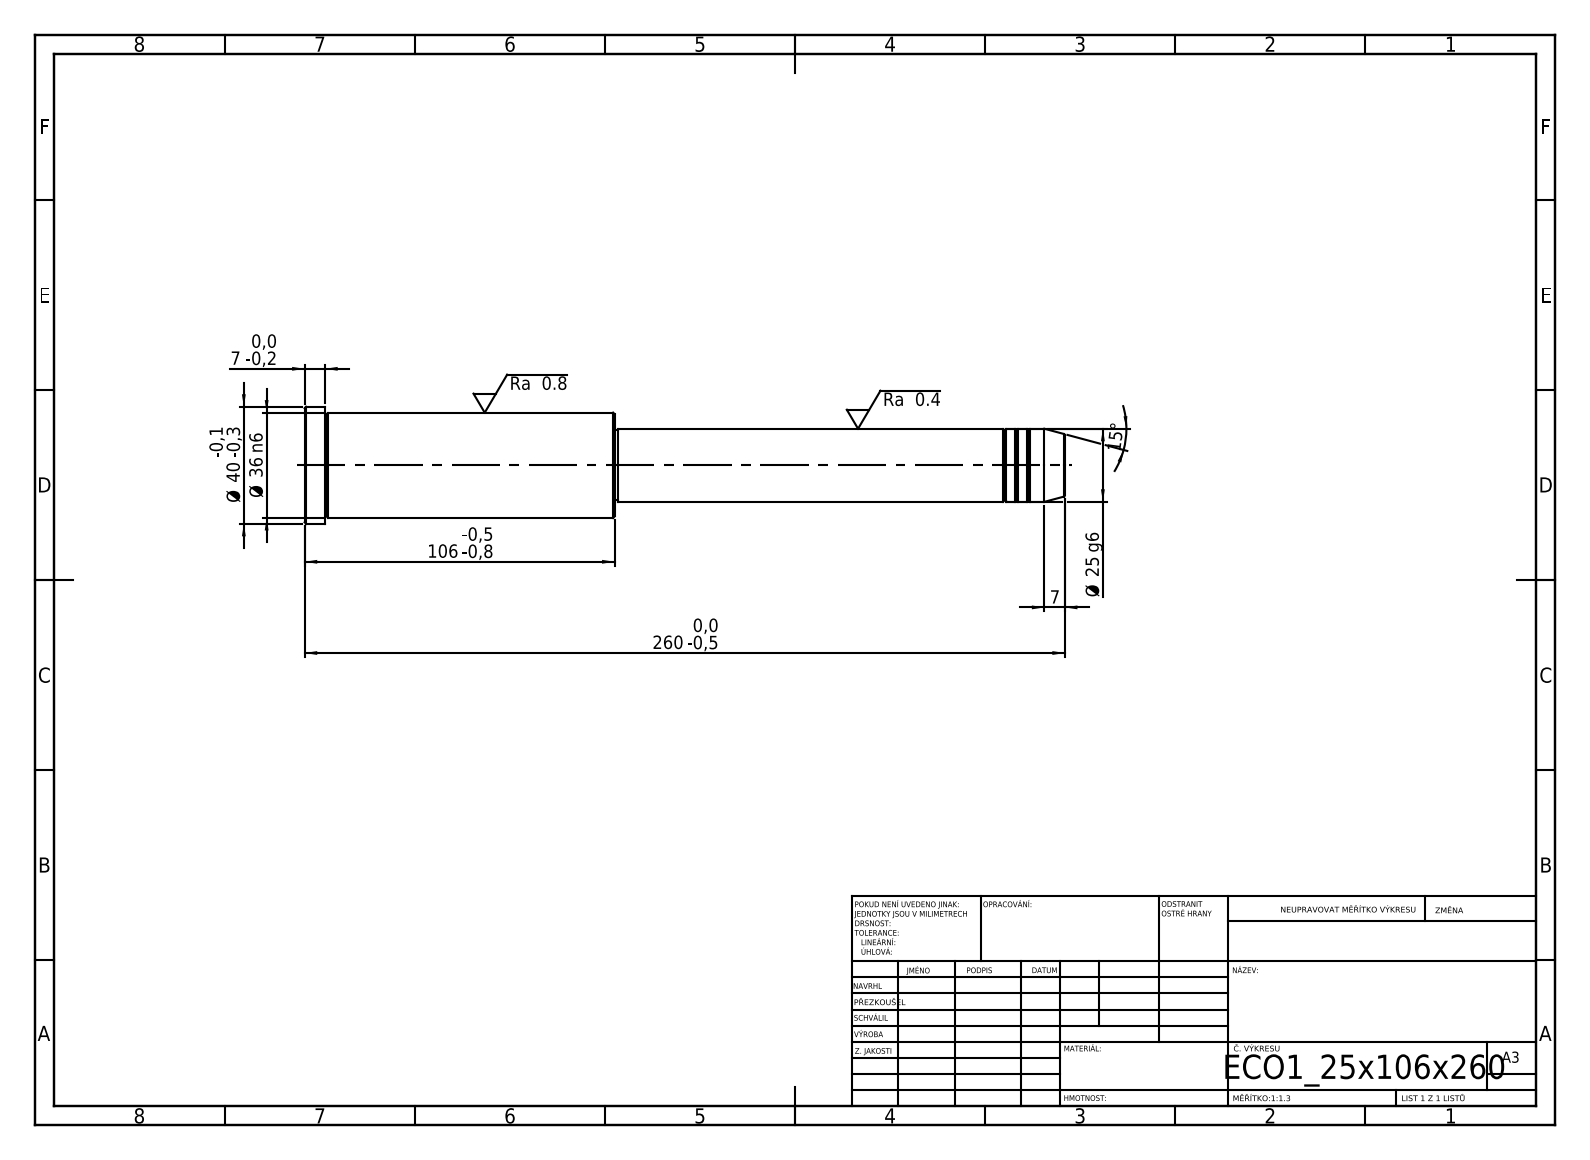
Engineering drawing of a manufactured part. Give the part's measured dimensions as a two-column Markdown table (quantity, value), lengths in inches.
| quantity | value |
| --- | --- |
| STEP written by | SolidWorks 2019 (CONFIG_CONTROL_DESIGN) |
| units | inches |
| bodies | 1 solid, 43 faces (5 planar, 14 cylindrical, 24 other) |
| overall size | 10.236 × 1.575 × 1.575 |
| volume | 11.26 in³ |
| surface area | 41.4 in² |
| round bosses / shafts (diameter × count) | 1.575 × 1, 1.417 × 1, 0.984 × 1, 0.945 × 1 |
| main face-to-face distances | 4.173, 6.063, 10.236, 9.961, 3.898, 0.276, 6.024, 0.039, 3.937, 4.213 |
